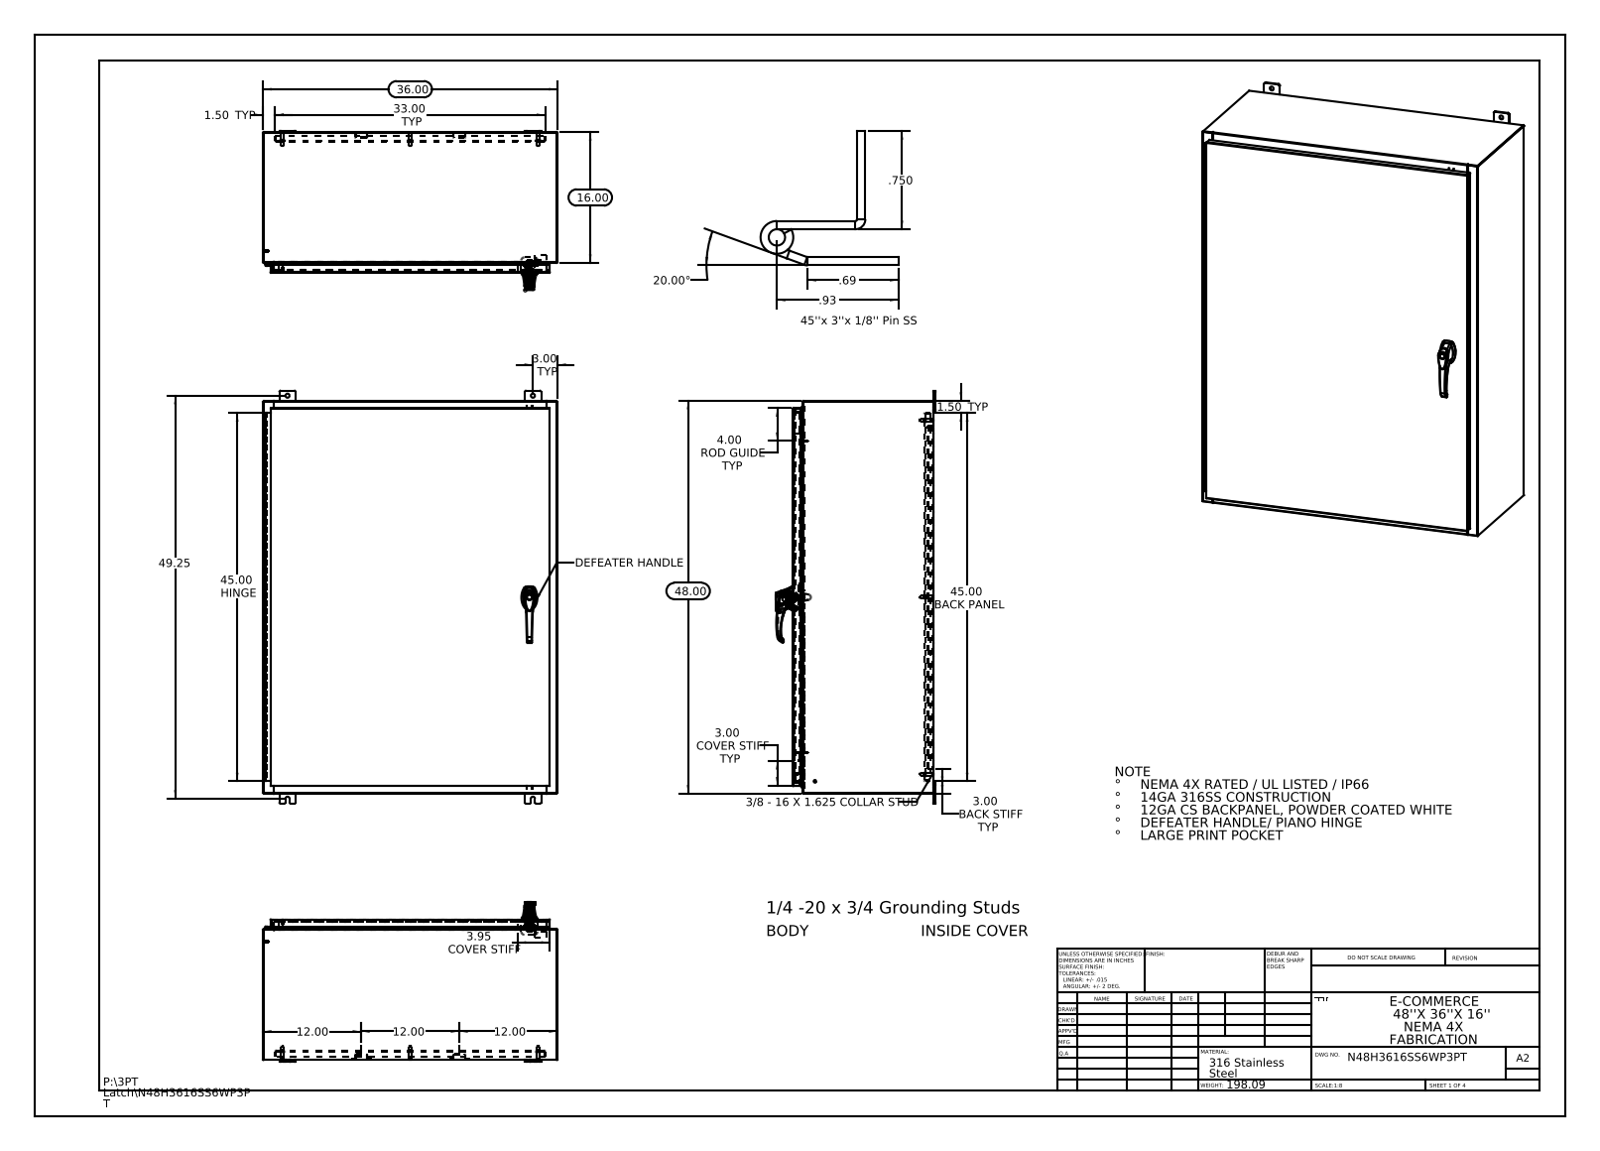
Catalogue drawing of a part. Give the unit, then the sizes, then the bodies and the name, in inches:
Units: inches
Overall size (bounding box): 50.5 × 36 × 19.495
Round holes (diameter × count): ⌀0.5 ×12, ⌀0.25 ×10, ⌀0.138 ×3, ⌀0.161 ×3, ⌀0.079 ×2, ⌀0.203 ×2, ⌀0.313 ×2, ⌀0.437 ×2, ⌀0.125 ×1, ⌀0.125 ×1, ⌀0.197 ×1, ⌀0.276 ×1
Round bosses / shafts (diameter × count): ⌀0.157 ×10, ⌀0.14 ×10, ⌀0.625 ×8, ⌀0.375 ×8, ⌀0.33 ×8, ⌀0.315 ×3, ⌀0.236 ×3, ⌀1.181 ×1
Partial cylindrical surfaces — rounded edges, fillets, slot ends (radius × count): R0.118 ×37, R0.013 ×34, R0.006 ×33, R0.088 ×28, R0.19 ×24, R0.039 ×15, R0.028 ×12, R0.008 ×6
Main face-to-face distances: 0.075, 17.126, 17.051, 17.201, 0.104, 35.925, 1, 16.126, 1.075, 16.051
Hole centre spacings: 17.357, 19.665, 21.625, 38.003, 45.986, 31.25, 43.25, 0.295
Volume: 706.2 in³ · Surface area: 17 651 in²
Bodies: 51 solids, 3400 faces (1309 planar, 1305 cylindrical, 786 other)
Part name (STEP PRODUCT): N48H3616SS6WP3PT 263033_Industrilas; N48H3616SS6WP3PT Defeater Handle Stiffener; 022151; 10_30 CD Stud (+8 more)
STEP written by: SolidWorks 2013 (CONFIG_CONTROL_DESIGN)
